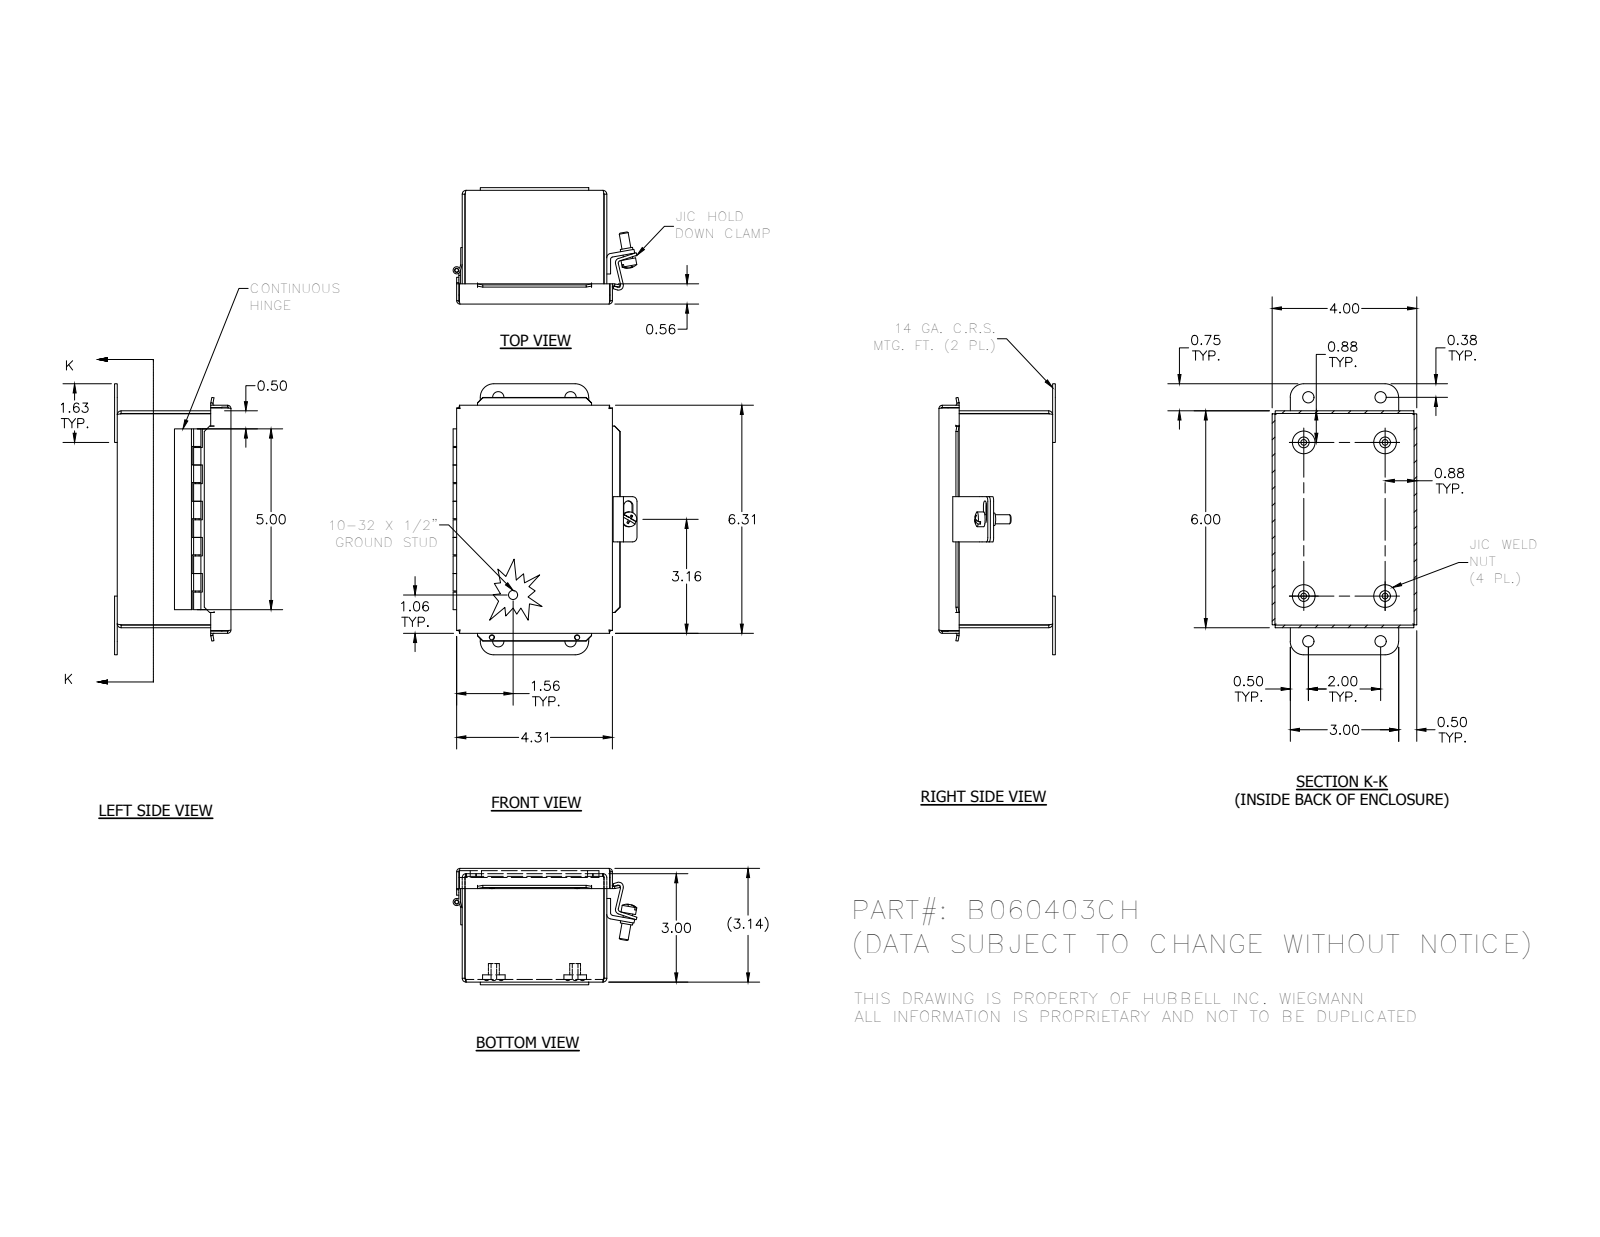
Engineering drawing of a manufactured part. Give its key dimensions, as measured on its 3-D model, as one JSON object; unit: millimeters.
{"part_name": "B060403CH; 3499; 3481; C1001 (+8 more)", "step_written_by": "Autodesk Inventor 2012 (AUTOMOTIVE_DESIGN)", "units": "millimeters", "bodies": {"solids": 17, "faces": 386, "planar": 253, "cylindrical": 91, "other": 42}, "overall_size": [190.5, 129.2, 81.8], "volume_mm3": 206300, "surface_area_mm2": 219700, "round_holes": [[4, 4], [7.9, 4], [3.6, 2], [2.9, 1], [5, 1]], "round_bosses_or_shafts": [[15.9, 4], [7.6, 4], [6.4, 2], [10.4, 1], [8.7, 1], [5.1, 1], [4.8, 1], [2.5, 1]], "partial_cylinders_radius": [[0.8, 15], [2.7, 8], [2.4, 7], [3.2, 4], [9.5, 4], [1.6, 3], [3.2, 3], [3.4, 2]], "face_to_face_distances": [1.9, 99.7, 78.3, 79.9, 1.6, 76.4, 78, 150.5, 101.6, 97.8], "hole_center_spacings": [62.6, 31.9, 31.9, 50.8, 139.8, 139.8, 149.8, 171.5]}
